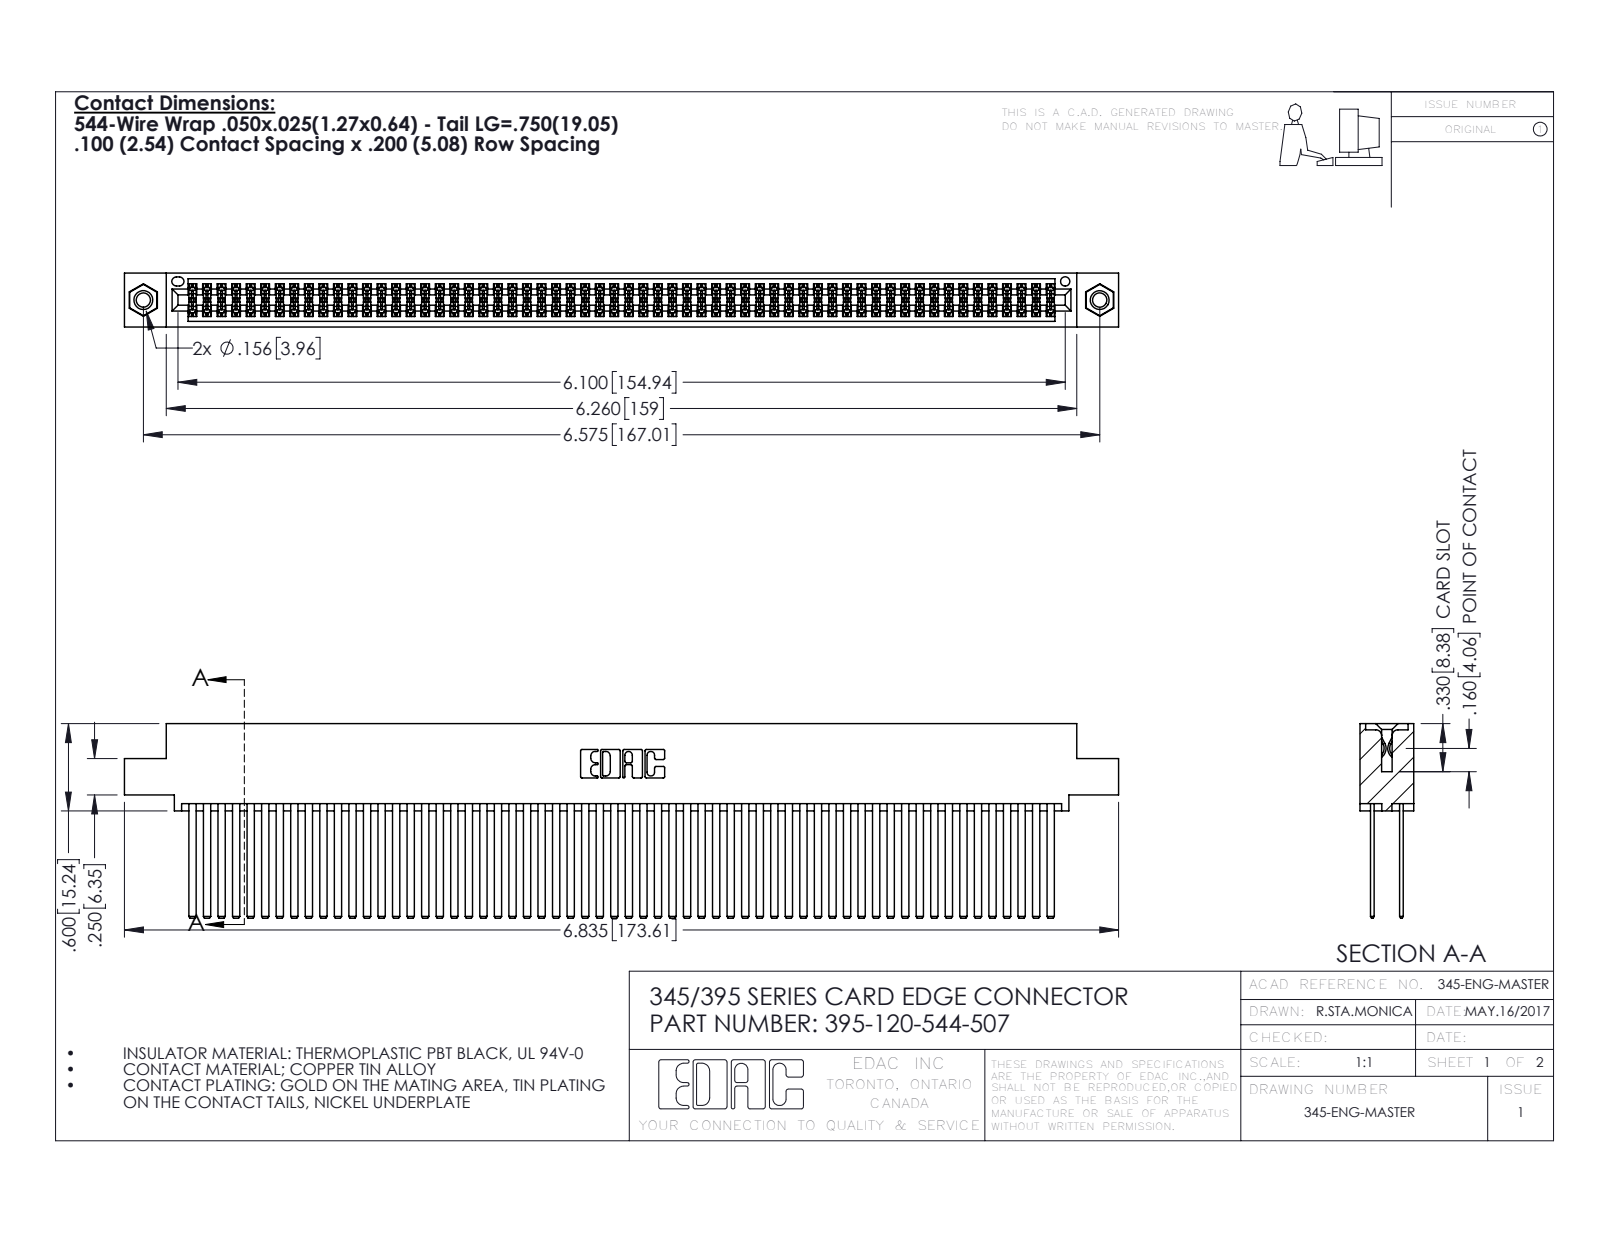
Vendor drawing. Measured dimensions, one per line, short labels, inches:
name: 345 Part_0.110 Offset - 0.156 Dia-TI; 345-292-001_345-293-144; 395-120-544-507; 345-250-001_345-250-005-103
written by: SolidWorks 2016 (CONFIG_CONTROL_DESIGN)
unit: in
bodies: 123 solids, 5470 faces (3596 planar, 1858 cylindrical, 16 other)
size: 6.835 × 1.337 × 0.37
volume: 1.137 in³; area: 51.05 in²
holes: 2× ⌀0.098, 2× ⌀0.125, 2× ⌀0.156, 1× ⌀0.064
bosses: 2× ⌀0.155
rounds: 180× R0.006, 22× R0.01, 6× R0.007, 6× R0.031, 3× R0.026, 2× R0.014, 2× R0.019, 2× R0.022
face distances: 0.2, 0.025, 0.072, 0.098, 0.272, 0.298, 0.225, 0.175, 0.37, 0.149
hole spacings: 0.27, 6.339, 6.575
